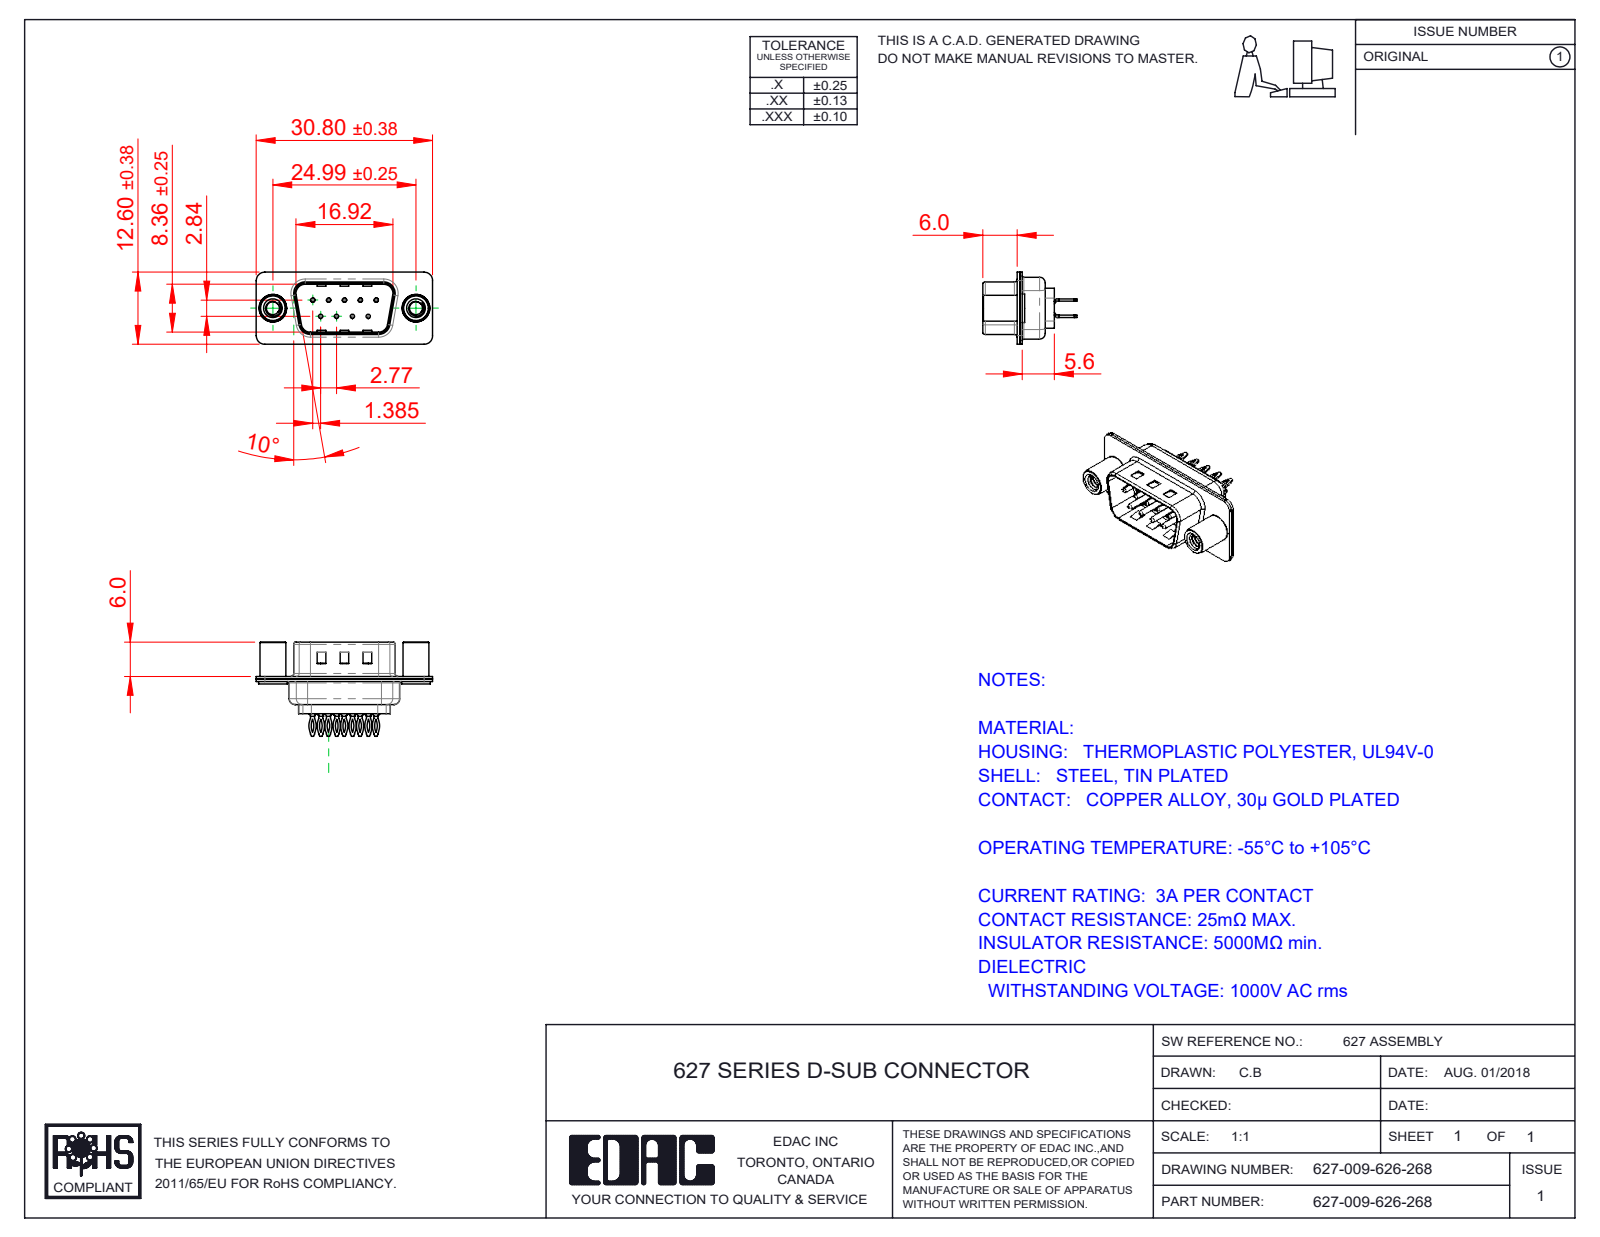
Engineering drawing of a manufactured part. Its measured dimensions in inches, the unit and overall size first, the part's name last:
Units: inches
Overall size (bounding box): 1.213 × 0.648 × 0.496
Round holes (diameter × count): ⌀0.014 ×9, ⌀0.043 ×9, ⌀0.063 ×9, ⌀0.089 ×2, ⌀0.157 ×2, ⌀0.189 ×2
Round bosses / shafts (diameter × count): ⌀0.079 ×9, ⌀0.059 ×9, ⌀0.03 ×9, ⌀0.197 ×2, ⌀0.193 ×2, ⌀0.177 ×2
Partial cylindrical surfaces — rounded edges, fillets, slot ends (radius × count): R0.059 ×18, R0.115 ×18, R0.131 ×18, R0.079 ×12, R0.02 ×8, R0.063 ×8, R0.01 ×4, R0.024 ×4
Main face-to-face distances: 0.016, 0.018, 0.035, 0.032, 0.377, 0.055, 0.345, 0.02, 0.059, 0.238
Hole centre spacings: 0.124, 0.109, 0.218, 0.198, 0.198, 0.327, 0.294, 0.295
Volume: 0.084 in³ · Surface area: 6.355 in²
Bodies: 14 solids, 1022 faces (289 planar, 436 cylindrical, 297 other)
Part name (STEP PRODUCT): 627 Shell Rear_09 Contacts; 627 Shell Front_09 Contacts; 627 Contact Row 1_26L; 627 Contact Row 2_26L (+3 more)
STEP written by: SolidWorks 2020 (CONFIG_CONTROL_DESIGN)
